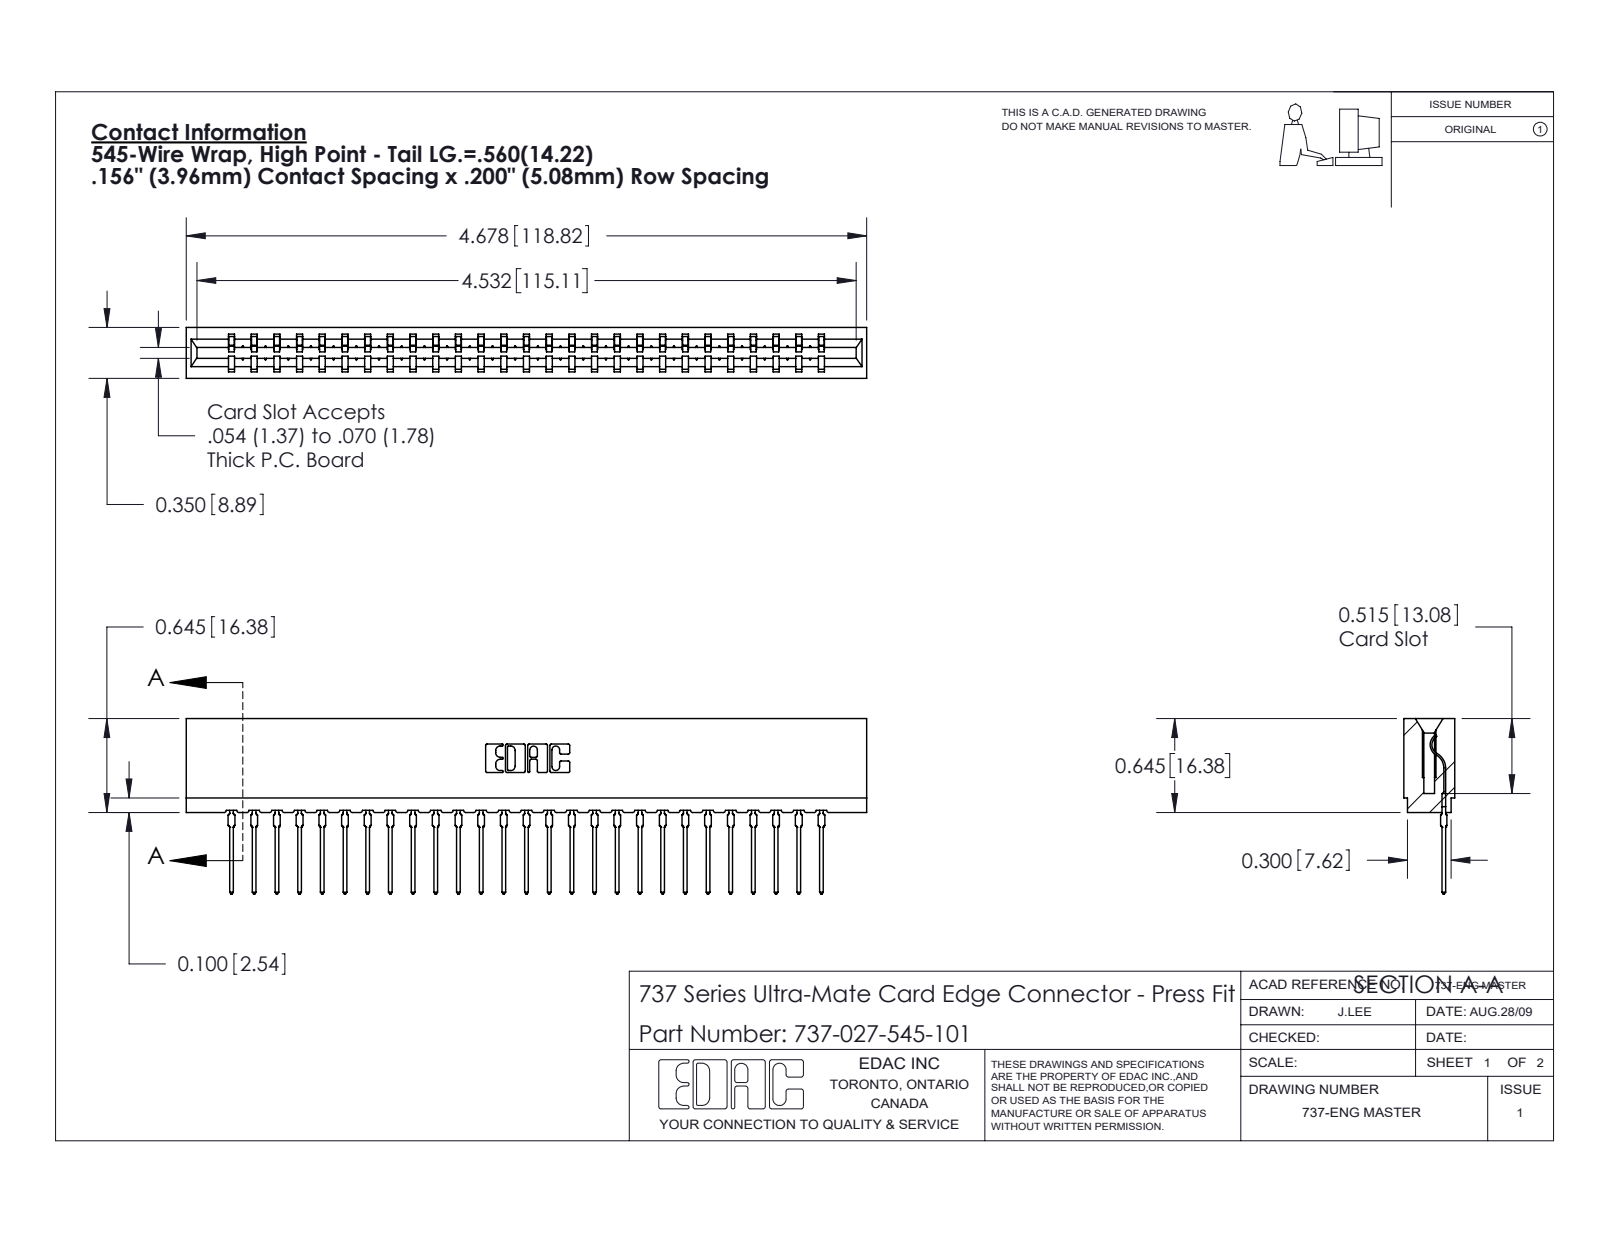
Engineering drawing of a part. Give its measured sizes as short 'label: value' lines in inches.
name: 745-292-001_545; 737 Part_Insulator Option - 01; 737-027-545-101
written by: SolidWorks 2020 (CONFIG_CONTROL_DESIGN)
unit: in
bodies: 28 solids, 3145 faces (1890 planar, 553 cylindrical, 702 other)
size: 4.678 × 1.206 × 0.35
volume: 0.712 in³; area: 24.55 in²
rounds: 54× R0.015, 54× R0.021, 22× R0.01, 6× R0.007, 6× R0.031, 4× R0.005, 4× R0.011, 3× R0.026
face distances: 0.138, 0.212, 0.35, 0.624, 0.156, 0.074, 0.78, 0.045, 0.305, 0.093
